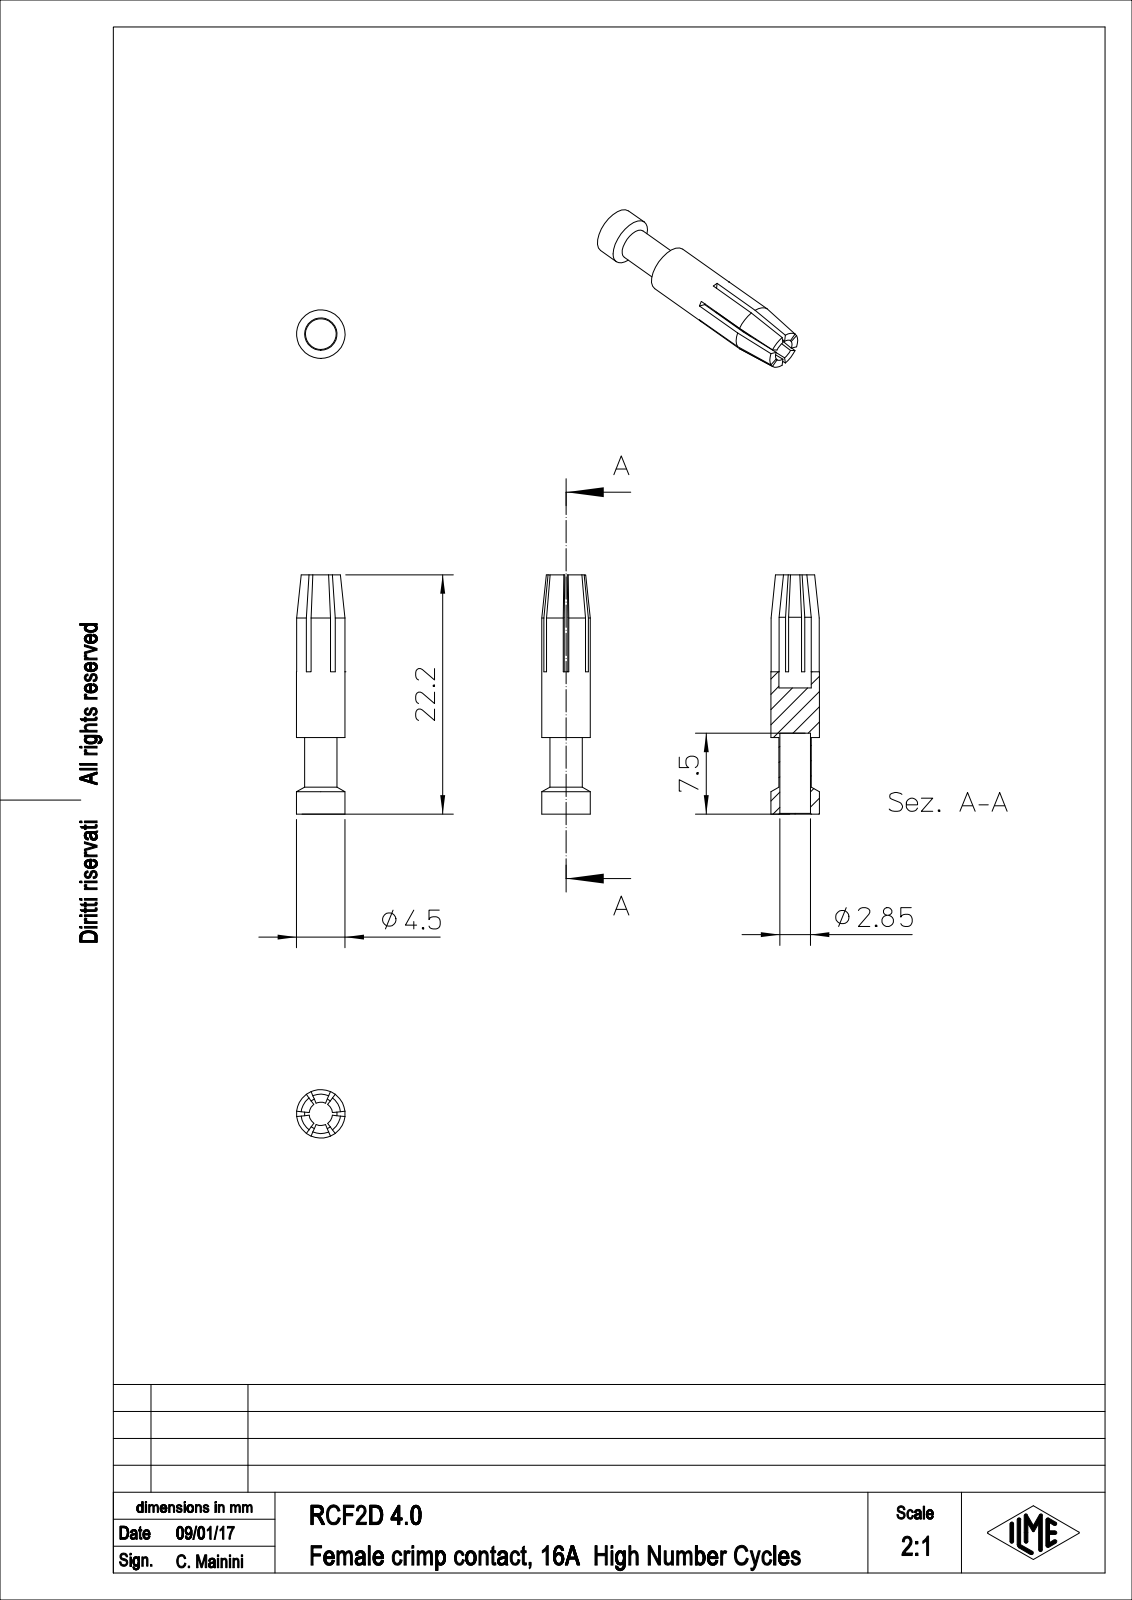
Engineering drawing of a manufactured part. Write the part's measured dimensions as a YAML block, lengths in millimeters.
part_name: "RCF2D_4.0"
step_written_by: "PTC Creo Elements/Direct Modeling 19.0E 27-Jun-2016 (C) Parametric Technology GmbH (AUTOMOTIVE_DESIGN)"
units: millimeters
bodies: {solids: 1, faces: 54, planar: 28, cylindrical: 10, other: 16}
overall_size: [22.2, 4.5, 4.5]
volume: 168
surface_area: 529
round_holes:
  - {diameter: 2.85, count: 1}
  - {diameter: 3, count: 1}
round_bosses_or_shafts:
  - {diameter: 4.5, count: 1}
face_to_face_distances: [7.1, 4.6, 11.7, 4.2, 0.4, 7.5, 10.5, 14.7, 15.1, 22.2]
